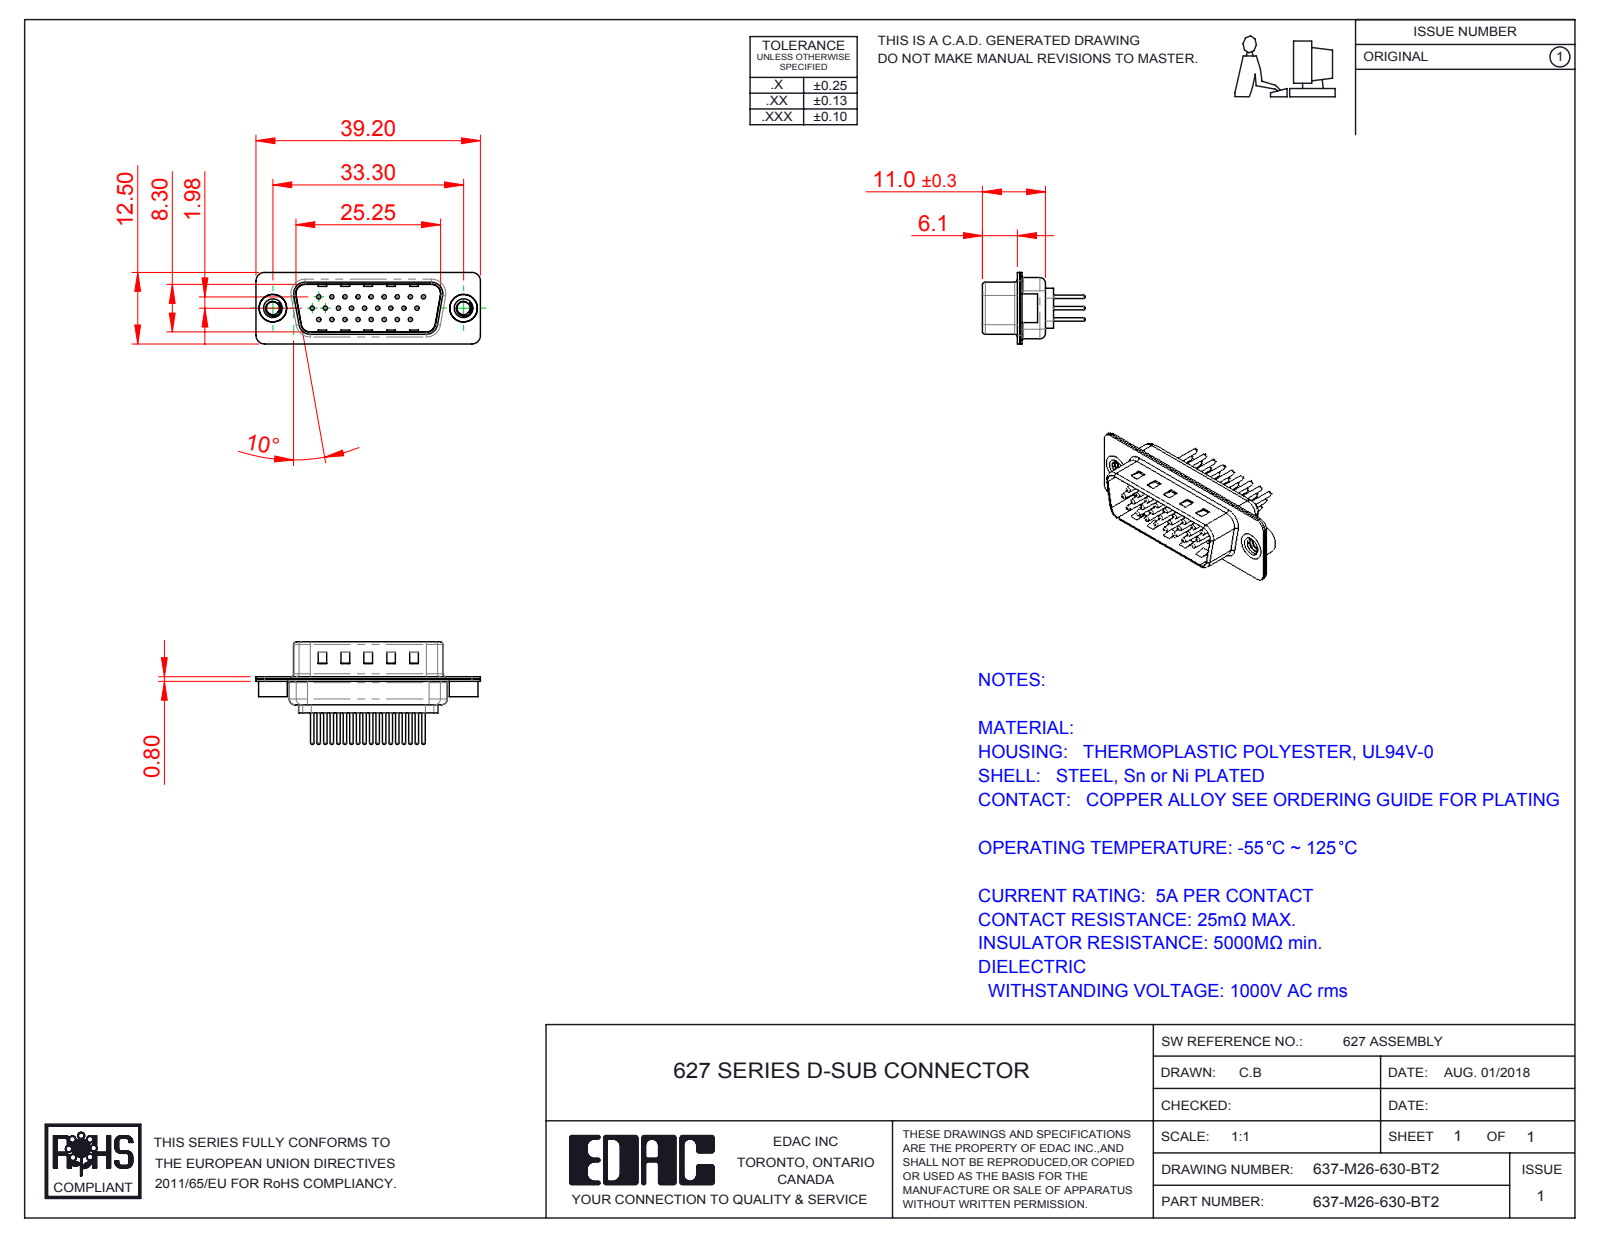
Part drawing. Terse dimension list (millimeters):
name: 637M Shell Front_26 Contacts; 637M Shell Rear_26 Contacts; 637M Contact Row 2_30; 637M Contact Row 1_30 (+4 more)
written by: SolidWorks 2016 (CONFIG_CONTROL_DESIGN)
unit: mm
bodies: 31 solids, 1302 faces (321 planar, 497 cylindrical, 484 other)
size: 39.2 × 17.9 × 12.5
volume: 1 909 mm³; area: 5 751 mm²
holes: 26× ⌀0.75, 26× ⌀1.6, 26× ⌀2, 2× ⌀2.26, 2× ⌀4, 2× ⌀4.8
bosses: 26× ⌀1.5, 26× ⌀0.6, 2× ⌀5, 2× ⌀4.9
rounds: 16× R1.5, 12× R2, 8× R0.5, 8× R1.6, 4× R0.25, 4× R0.6, 4× R0.65, 4× R0.9
face distances: 0.4, 0.8, 9.5, 9.1, 8.7, 9.9, 0.75, 5.5, 0.35, 5.9
hole spacings: 3.96, 2.28, 4.57, 6.05, 2.29, 8.24, 6.86, 10.48
